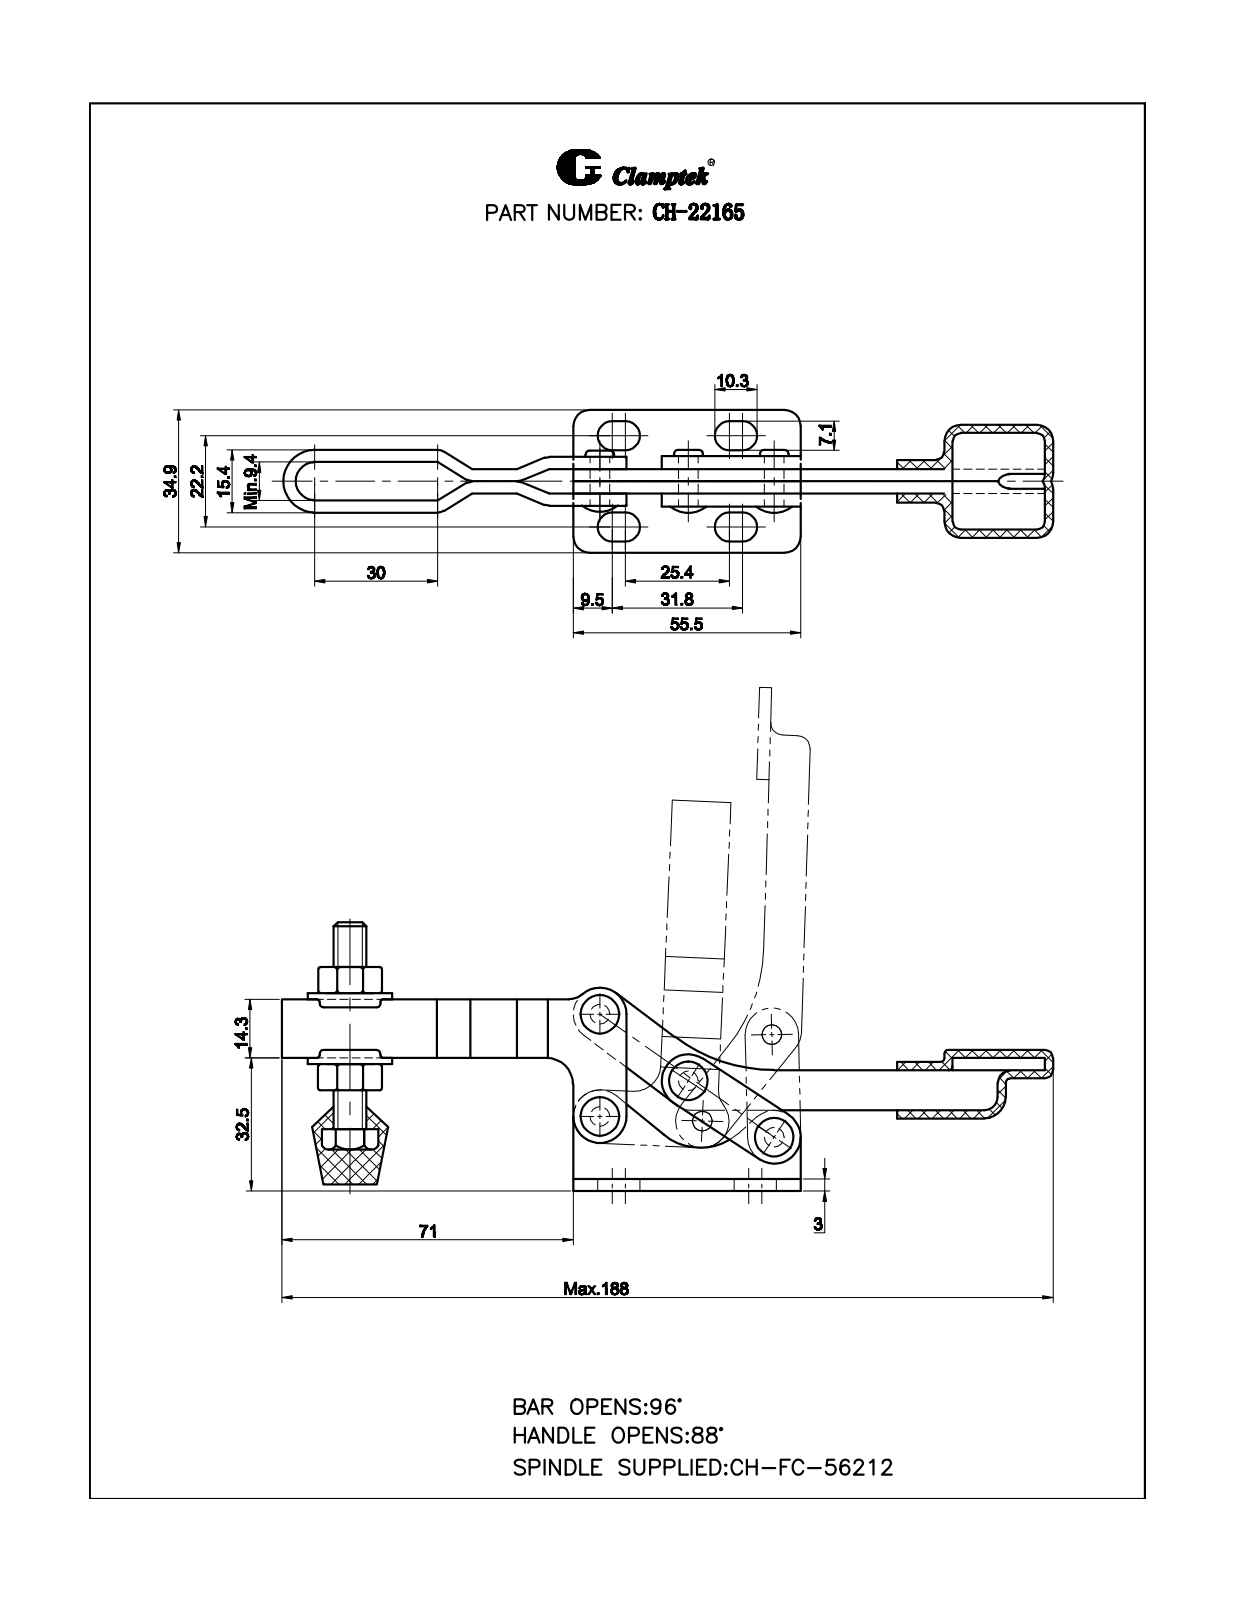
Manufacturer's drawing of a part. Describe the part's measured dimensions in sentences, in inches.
The part is named "22165-04_??; 22165-01_??; CH-22165; FC-56212_?? (+6 more)". Its 3-D file was written by "SolidWorks 2005179 (CONFIG_CONTROL_DESIGN)". It is 17 solids with 852 faces: 312 planar, 266 cylindrical and 274 other. Overall it measures 7.266 by 2.5 by 1.374 inches. Its volume is 2.634 cubic inches and its surface area 59.27 square inches. Round holes: 4 of diameter 0.137, 4 of diameter 0.189, 1 of diameter 0.152, 1 of diameter 0.248, 1 of diameter 0.319. Round bosses or shafts: 4 of diameter 0.335, 4 of diameter 0.185, 1 of diameter 0.512, 1 of diameter 0.312, 1 of diameter 0.101. Partial cylindrical surfaces (rounded edges, fillets, slot ends): 34 of radius 0.079, 11 of radius 0.118, 8 of radius 0.14, 4 of radius 0.157, 4 of radius 0.256, 2 of radius 0.039, 2 of radius 0.197, 1 of radius 0.126. The main face-to-face distances are 0.118, 0.236, 0.079, 0.354, 0.472, 0.039, 0.563, 0.07, 0.402, 0.048. The hole center spacings are 0.984, 0.917, 1.065, 1.685, 2.048, 2.641, 2.806, 3.543.
